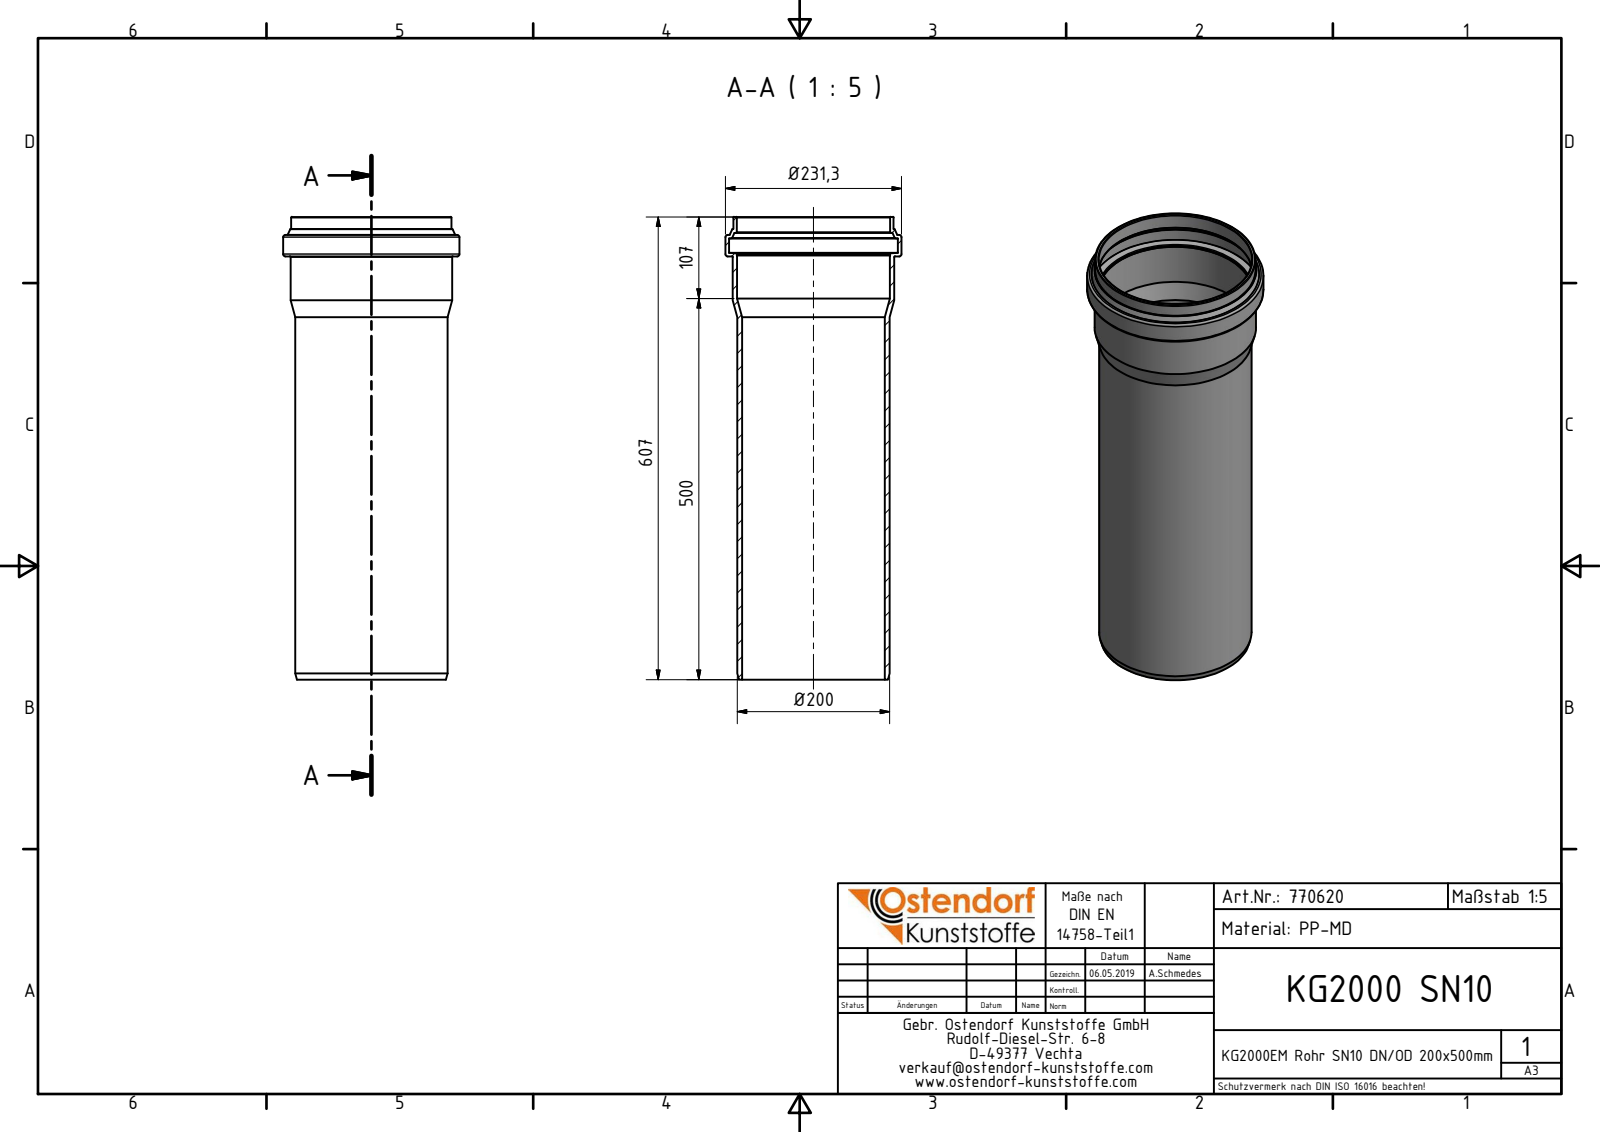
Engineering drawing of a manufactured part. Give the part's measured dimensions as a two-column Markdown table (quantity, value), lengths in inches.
| quantity | value |
| --- | --- |
| part name | 770620 KG2000EM Rohr SN10 DN-OD200x500 |
| STEP written by | Autodesk Inventor 2016 (AUTOMOTIVE_DESIGN) |
| units | inches |
| bodies | 1 solid, 37 faces (6 planar, 9 cylindrical, 22 other) |
| overall size | 23.898 × 9.106 × 9.106 |
| volume | 140.5 in³ |
| surface area | 1 207 in² |
| round holes (diameter × count) | 7.386 × 1, 7.906 × 1, 7.913 × 1, 8.736 × 1 |
| round bosses / shafts (diameter × count) | 9.106 × 1, 8.346 × 1, 8.283 × 1, 7.874 × 1 |
| main face-to-face distances | 21.862, 22.972, 1.11, 23.898, 2.035, 0.925, 23.267, 1.404, 0.294, 0.631 |
